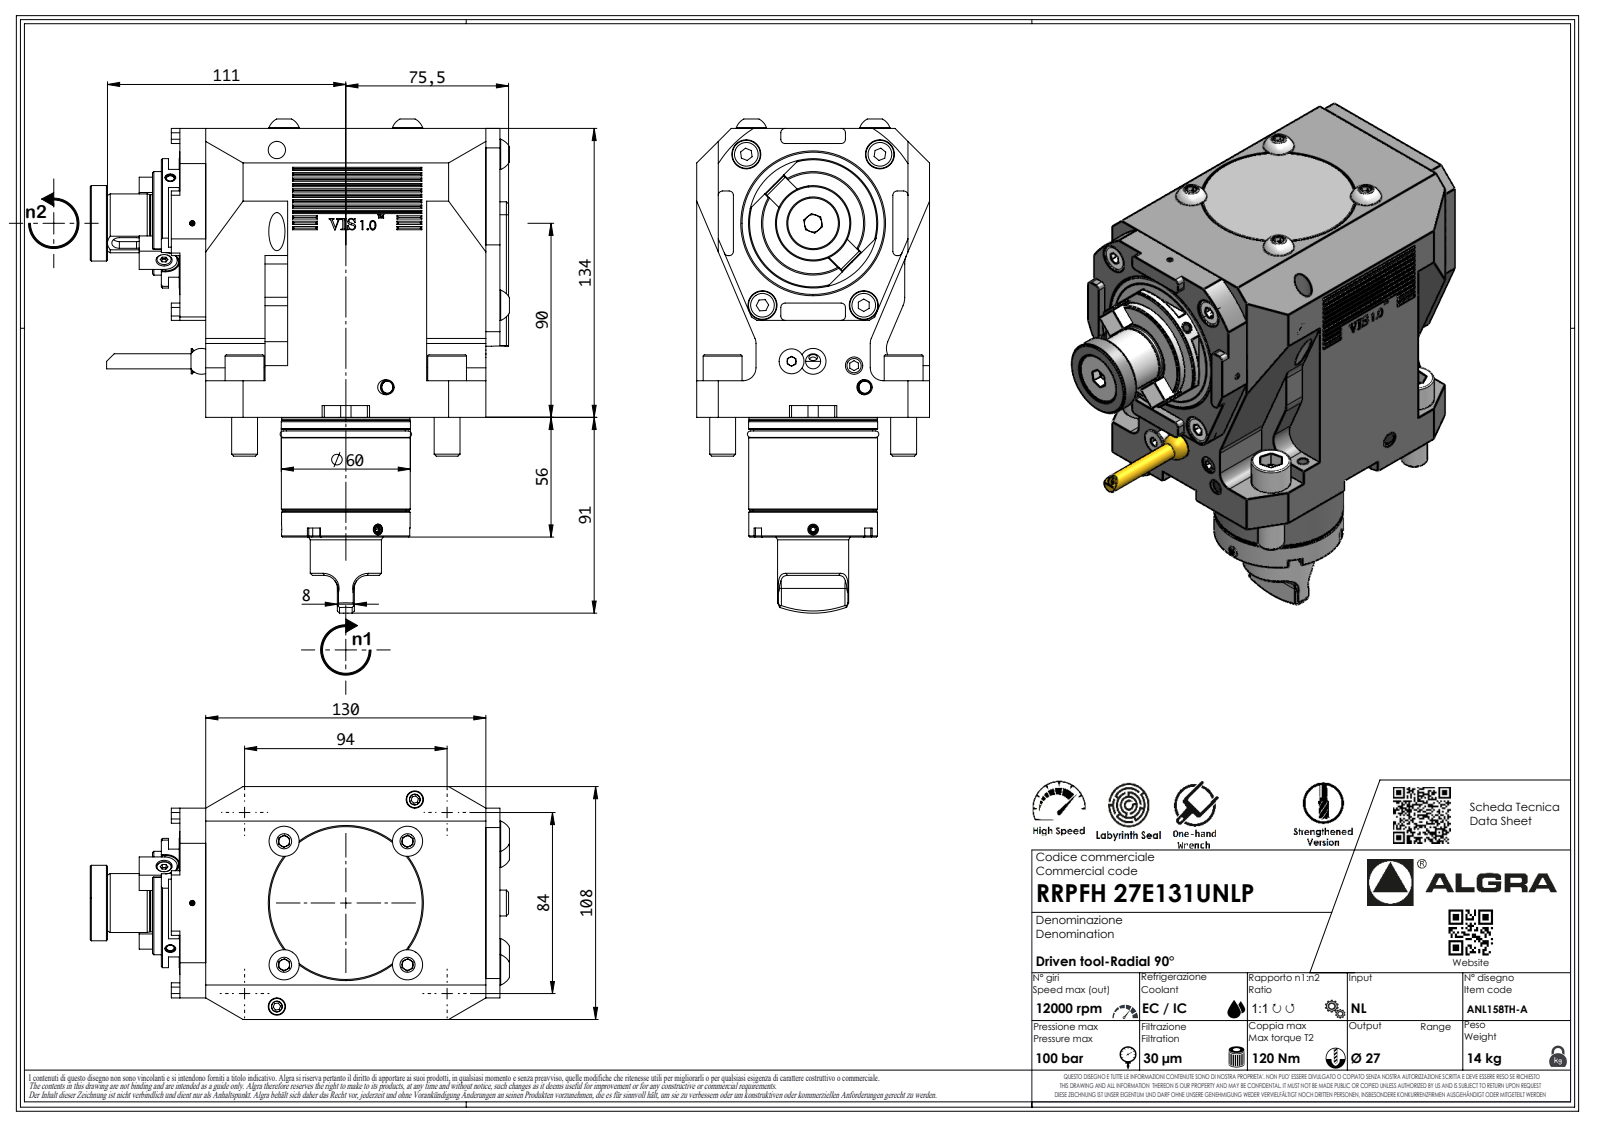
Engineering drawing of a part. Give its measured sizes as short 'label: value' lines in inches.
name: RRPFH27E131UNLP
written by: SolidWorks 2023 (AUTOMOTIVE_DESIGN)
unit: in
bodies: 1 solid, 1028 faces (706 planar, 139 cylindrical, 183 other)
size: 8.85 × 7.642 × 4.252
volume: 124 in³; area: 203.2 in²
holes: 1× ⌀0.083, 1× ⌀0.157
bosses: 4× ⌀0.709, 4× ⌀0.472, 1× ⌀2.362, 1× ⌀2.358, 1× ⌀2.354, 1× ⌀2.35, 1× ⌀2.343, 1× ⌀2.173
rounds: 21× R0.008, 18× R0.315, 16× R0.079, 15× R0.236, 7× R0.013, 7× R0.02, 7× R0.146, 4× R0.394
face distances: 4.252, 5.276, 0.472, 1.083, 4.035, 0.256, 5.374, 1.496, 0.217, 5.846
